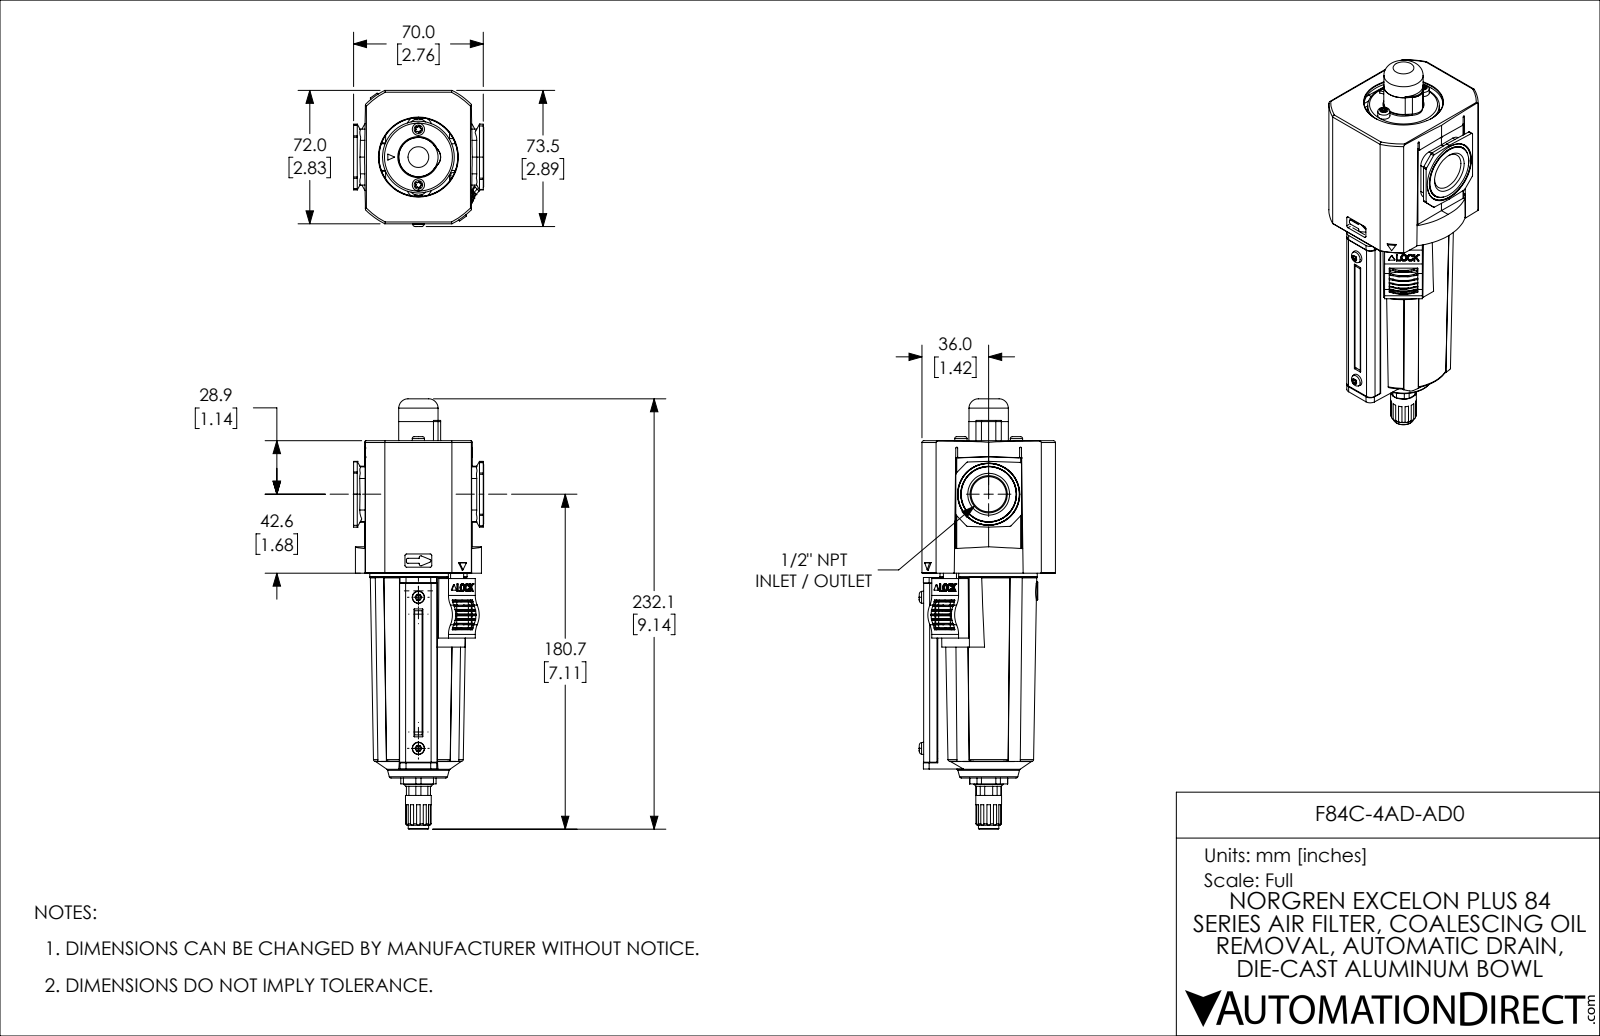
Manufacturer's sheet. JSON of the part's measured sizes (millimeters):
{"part_name": "F84C-4AD-AD0", "step_written_by": "SolidWorks 2021 (CONFIG_CONTROL_DESIGN)", "units": "millimeters", "bodies": {"solids": 8, "faces": 1363, "planar": 594, "cylindrical": 515, "other": 254}, "overall_size": [232.1, 73.5, 70.3], "volume_mm3": 484600, "surface_area_mm2": 112600, "round_holes": [[2.8, 2], [4.1, 2], [4.5, 2], [5.6, 1], [6.2, 1], [16.1, 1], [19.7, 1], [62.5, 1]], "round_bosses_or_shafts": [[8, 2], [7, 2], [6.6, 2], [5.4, 2], [53.9, 1], [52.5, 1], [51.3, 1], [49.8, 1]], "partial_cylinders_radius": [[1, 58], [0.5, 57], [0.7, 28], [0.3, 18], [0.2, 8], [1, 8], [1.1, 8], [1.5, 8]], "face_to_face_distances": [52, 9.6, 62.4, 72, 61.2, 49.6, 11.7, 1.5, 9.2, 40.3], "hole_center_spacings": [15, 15.1, 30.1, 30, 30.2, 63.6]}
